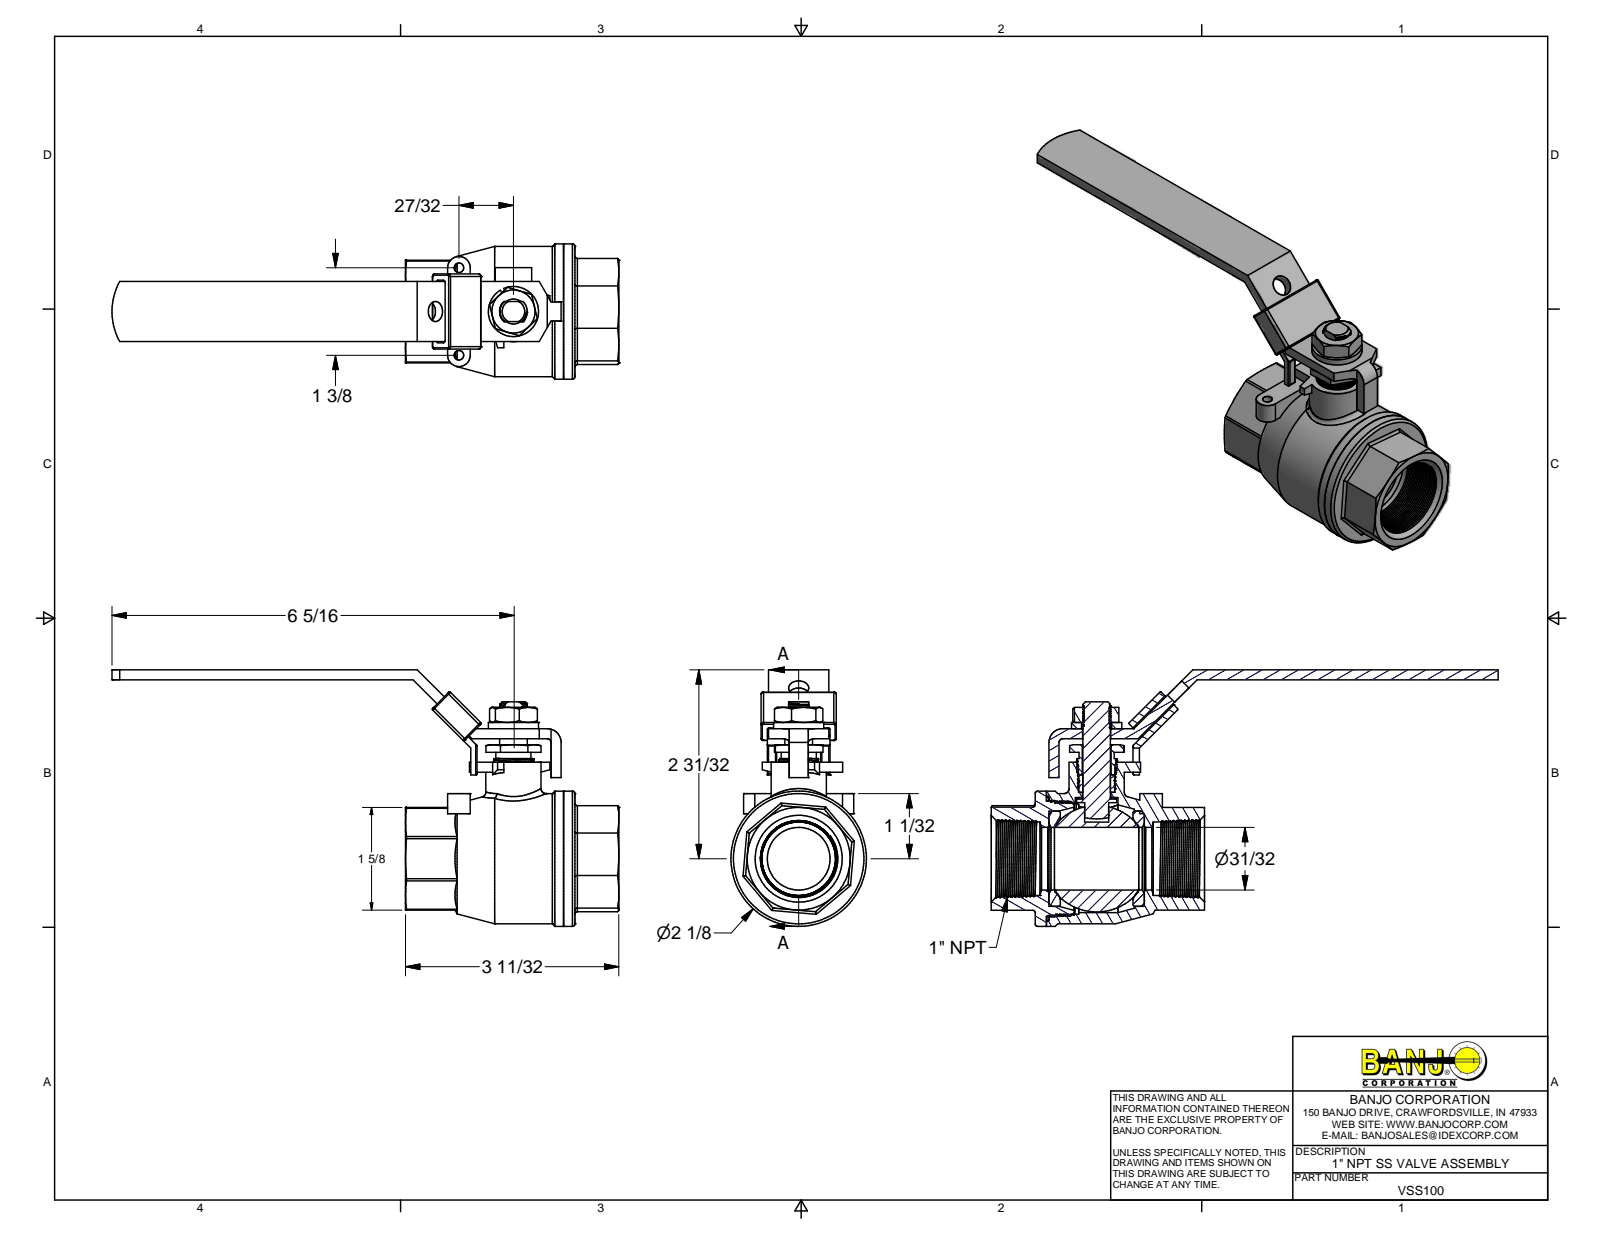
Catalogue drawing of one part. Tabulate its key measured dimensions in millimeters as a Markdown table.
| quantity | value |
| --- | --- |
| part name | VSS100 |
| STEP written by | Autodesk Inventor 2013 (AUTOMOTIVE_DESIGN) |
| units | millimeters |
| bodies | 14 solids, 387 faces (144 planar, 116 cylindrical, 127 other) |
| overall size | 202 × 102.4 × 54 |
| volume | 125 903 mm³ |
| surface area | 67 452 mm² |
| round holes (diameter × count) | 3.8 × 2, 8 × 1, 9.92 × 1, 11.4 × 1, 11.5 × 1, 12 × 1, 14.5 × 1, 17 × 1, 25 × 1, 38 × 1, 42.98 × 1, 44.3 × 1 |
| round bosses / shafts (diameter × count) | 54 × 1, 52 × 1, 49 × 1, 46 × 1, 22 × 1, 20 × 1, 16 × 1, 15.87 × 1 |
| partial cylindrical surfaces (radius × count) | 1 × 16, 0.5 × 15, 4.5 × 2, 25 × 2, 1.5 × 1, 5.5 × 1, 5.6 × 1, 22 × 1 |
| main face-to-face distances | 4, 4.5, 2.5, 23.5, 0.5, 5.5, 3, 24, 27.5, 7 |
| hole center spacings | 27.87, 34.92 |
